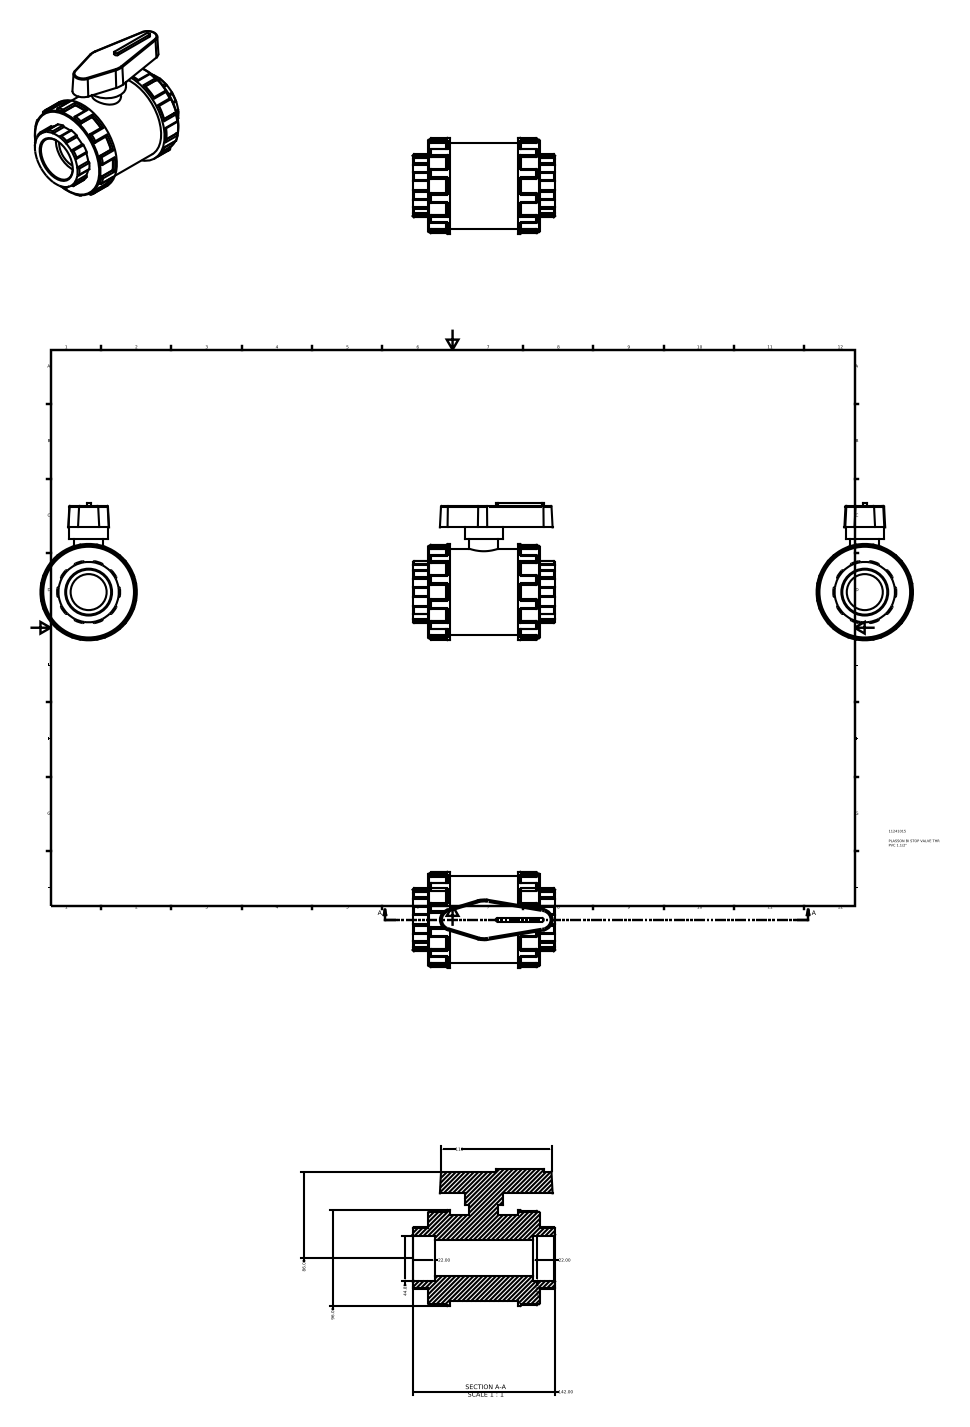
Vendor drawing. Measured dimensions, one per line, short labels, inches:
name: 11241015
written by: Autodesk Inventor 2015 (AUTOMOTIVE_DESIGN)
unit: in
bodies: 1 solid, 434 faces (114 planar, 192 cylindrical, 128 other)
size: 5.591 × 5.377 × 3.78
volume: 43.23 in³; area: 128.8 in²
holes: 1× ⌀1.413, 1× ⌀1.765
bosses: 1× ⌀3.78, 1× ⌀3.628, 1× ⌀3.402, 1× ⌀1.512, 1× ⌀1.134
rounds: 68× R0.053, 4× R0.035, 2× R0.076, 1× R1.183, 1× R1.236
face distances: 0.866, 4.378, 0.606, 4.118, 3.512, 1.472, 4.984, 0.846, 2.646, 4.724
